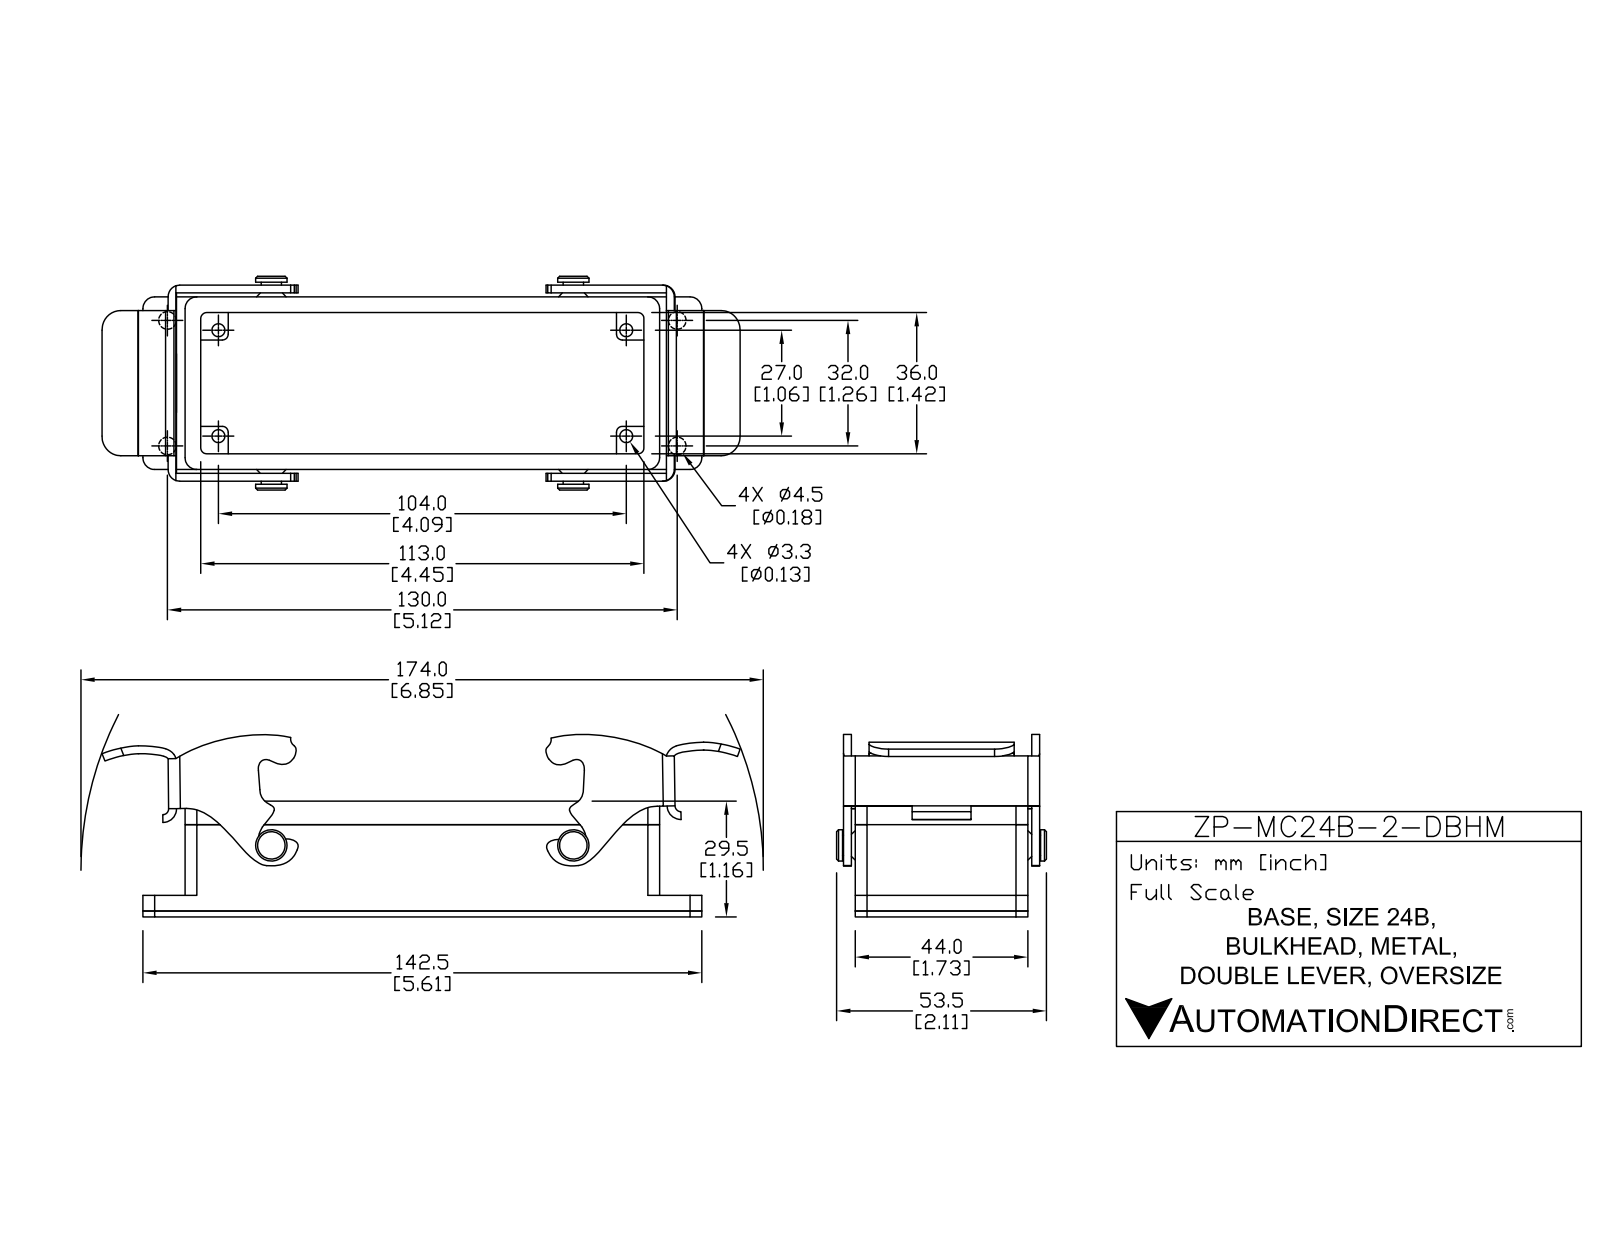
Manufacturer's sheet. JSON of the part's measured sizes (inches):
{"part_name": "ZP-MC24B-2-DBHM", "step_written_by": "SolidWorks 2011 (AUTOMOTIVE_DESIGN)", "units": "inches", "bodies": {"solids": 9, "faces": 314, "planar": 130, "cylindrical": 176, "other": 8}, "overall_size": [6.827, 2.146, 1.719], "volume_in3": 2.752, "surface_area_in2": 65.25, "round_holes": [[0.13, 4], [0.177, 4]], "round_bosses_or_shafts": [[0.315, 2], [0.204, 2]], "partial_cylinders_radius": [[0.02, 26], [0.059, 12], [0.118, 10], [0.079, 6], [0.157, 6], [0.039, 4], [0.394, 4], [0.036, 2]], "face_to_face_distances": [0.157, 0.118, 0.039, 1.732, 0.045, 1.614, 1.575, 1.457, 0.866, 0.207], "hole_center_spacings": [0.521, 1.269, 4.607, 4.75, 1.063, 1.26, 4.094, 4.23]}
